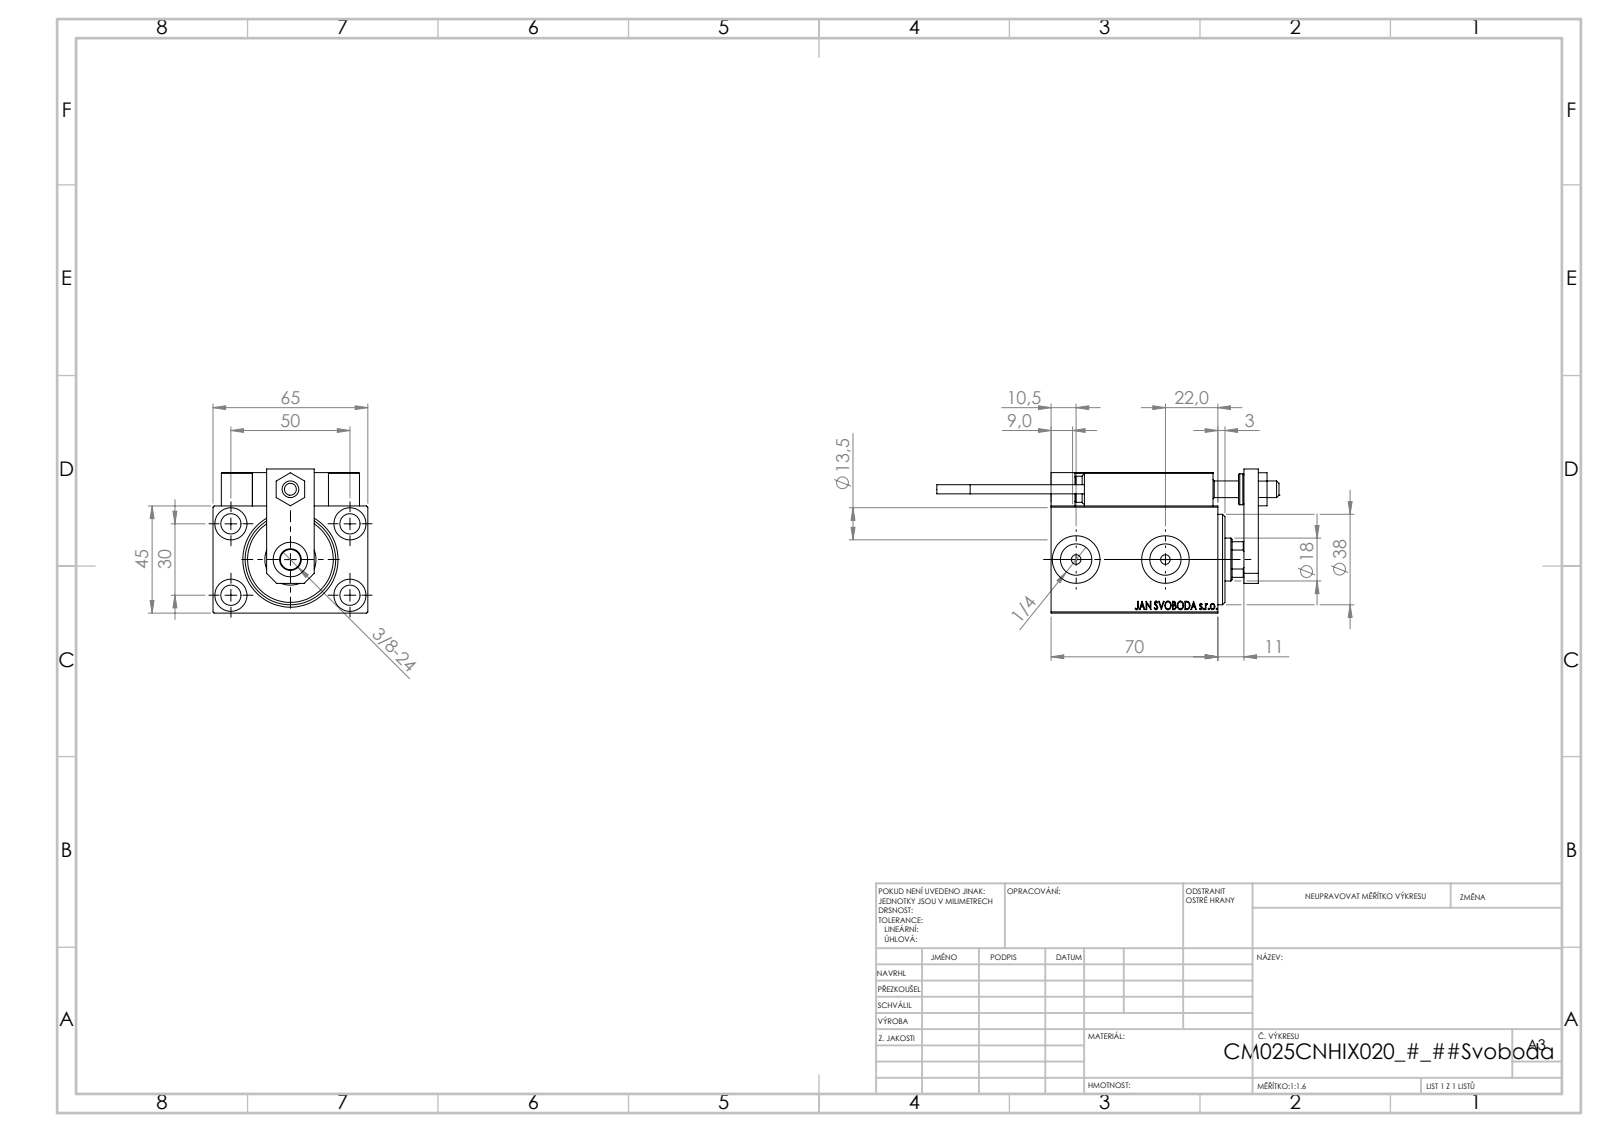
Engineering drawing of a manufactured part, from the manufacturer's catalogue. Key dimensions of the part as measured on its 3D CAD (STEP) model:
Part name (STEP PRODUCT): Block; TYC_L79; ALLEN BOLT D5; V450CM_VC_B (+7 more)
STEP written by: SolidWorks 2019 (CONFIG_CONTROL_DESIGN)
Units: millimetres
Bodies: 23 solids, 1282 faces (560 planar, 188 cylindrical, 534 other)
Overall size (bounding box): 143.7 × 65 × 60.5
Volume: 223 110 mm³ · Surface area: 69 190 mm²
Round holes (diameter × count): ⌀4 ×6, ⌀8 ×5, ⌀8.5 ×5, ⌀3.2 ×4, ⌀13.5 ×4, ⌀5 ×2, ⌀13.16 ×2, ⌀20 ×2, ⌀7 ×1, ⌀14.5 ×1, ⌀18 ×1, ⌀21.5 ×1
Round bosses / shafts (diameter × count): ⌀5 ×2, ⌀3.8 ×2, ⌀13 ×1, ⌀11 ×1
Partial cylindrical surfaces — rounded edges, fillets, slot ends (radius × count): R0.3 ×30, R3 ×2, R8.5 ×1
Main face-to-face distances: 45, 59, 14, 65, 6, 3, 19, 5, 13, 7
Hole centre spacings: 29.15, 11.37, 20, 22.09, 28.9, 29.59, 29.69, 30
